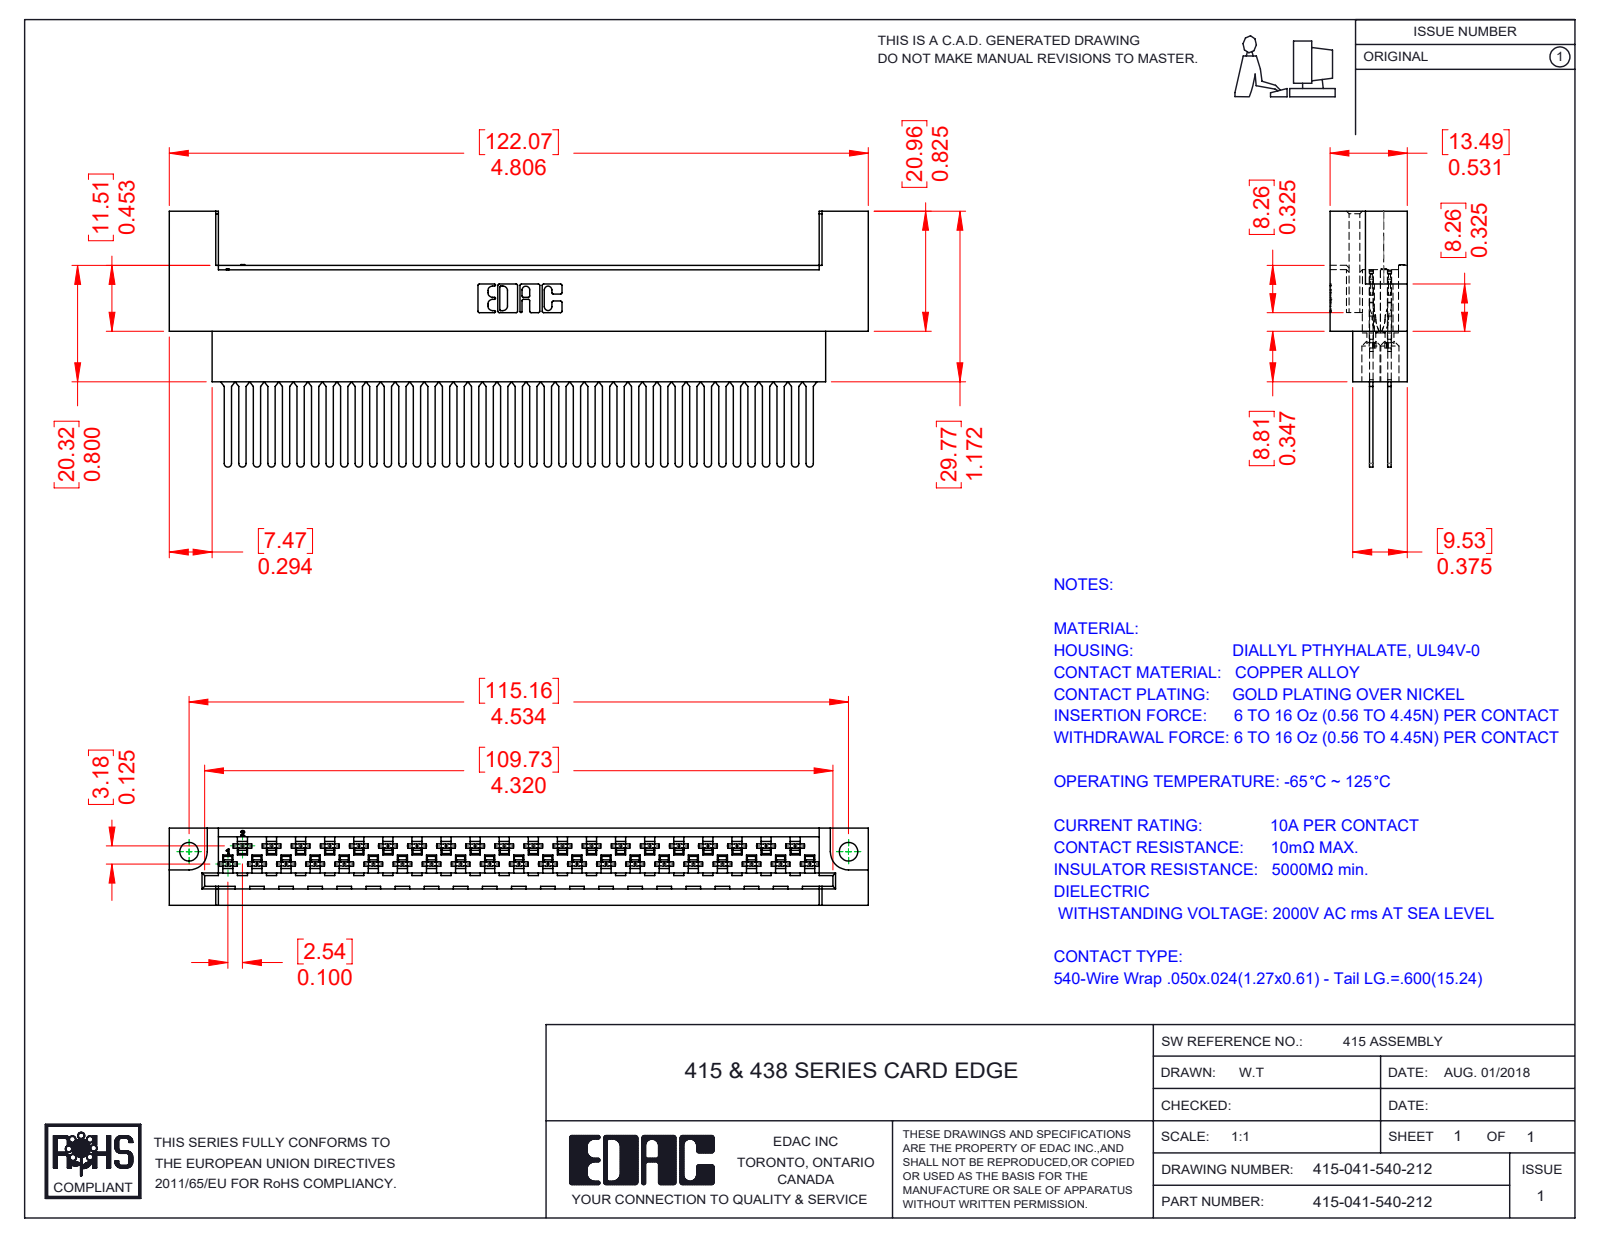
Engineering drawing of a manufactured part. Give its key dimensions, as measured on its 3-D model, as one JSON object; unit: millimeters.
{"part_name": "415-041-540-212; 516-290-001_540; 415-210-001_415-210-041-212", "step_written_by": "SolidWorks 2016 (CONFIG_CONTROL_DESIGN)", "units": "millimeters", "bodies": {"solids": 42, "faces": 4178, "planar": 2675, "cylindrical": 1112, "other": 391}, "overall_size": [122.07, 44.66, 13.49], "volume_mm3": 21935, "surface_area_mm2": 28215, "round_holes": [[1.27, 41], [3.3, 41], [3.25, 2]], "partial_cylinders_radius": [[0.3, 164], [0.56, 164], [0.18, 82], [0.2, 82], [0.41, 82], [2.03, 82], [0.64, 41], [0.25, 22]], "face_to_face_distances": [3.18, 0.61, 1.88, 7.49, 13.49, 1.27, 6.61, 6.88, 6, 2.82], "hole_center_spacings": [5.08, 10.16, 15.24, 20.32, 25.4, 30.48, 35.56, 2.54]}
